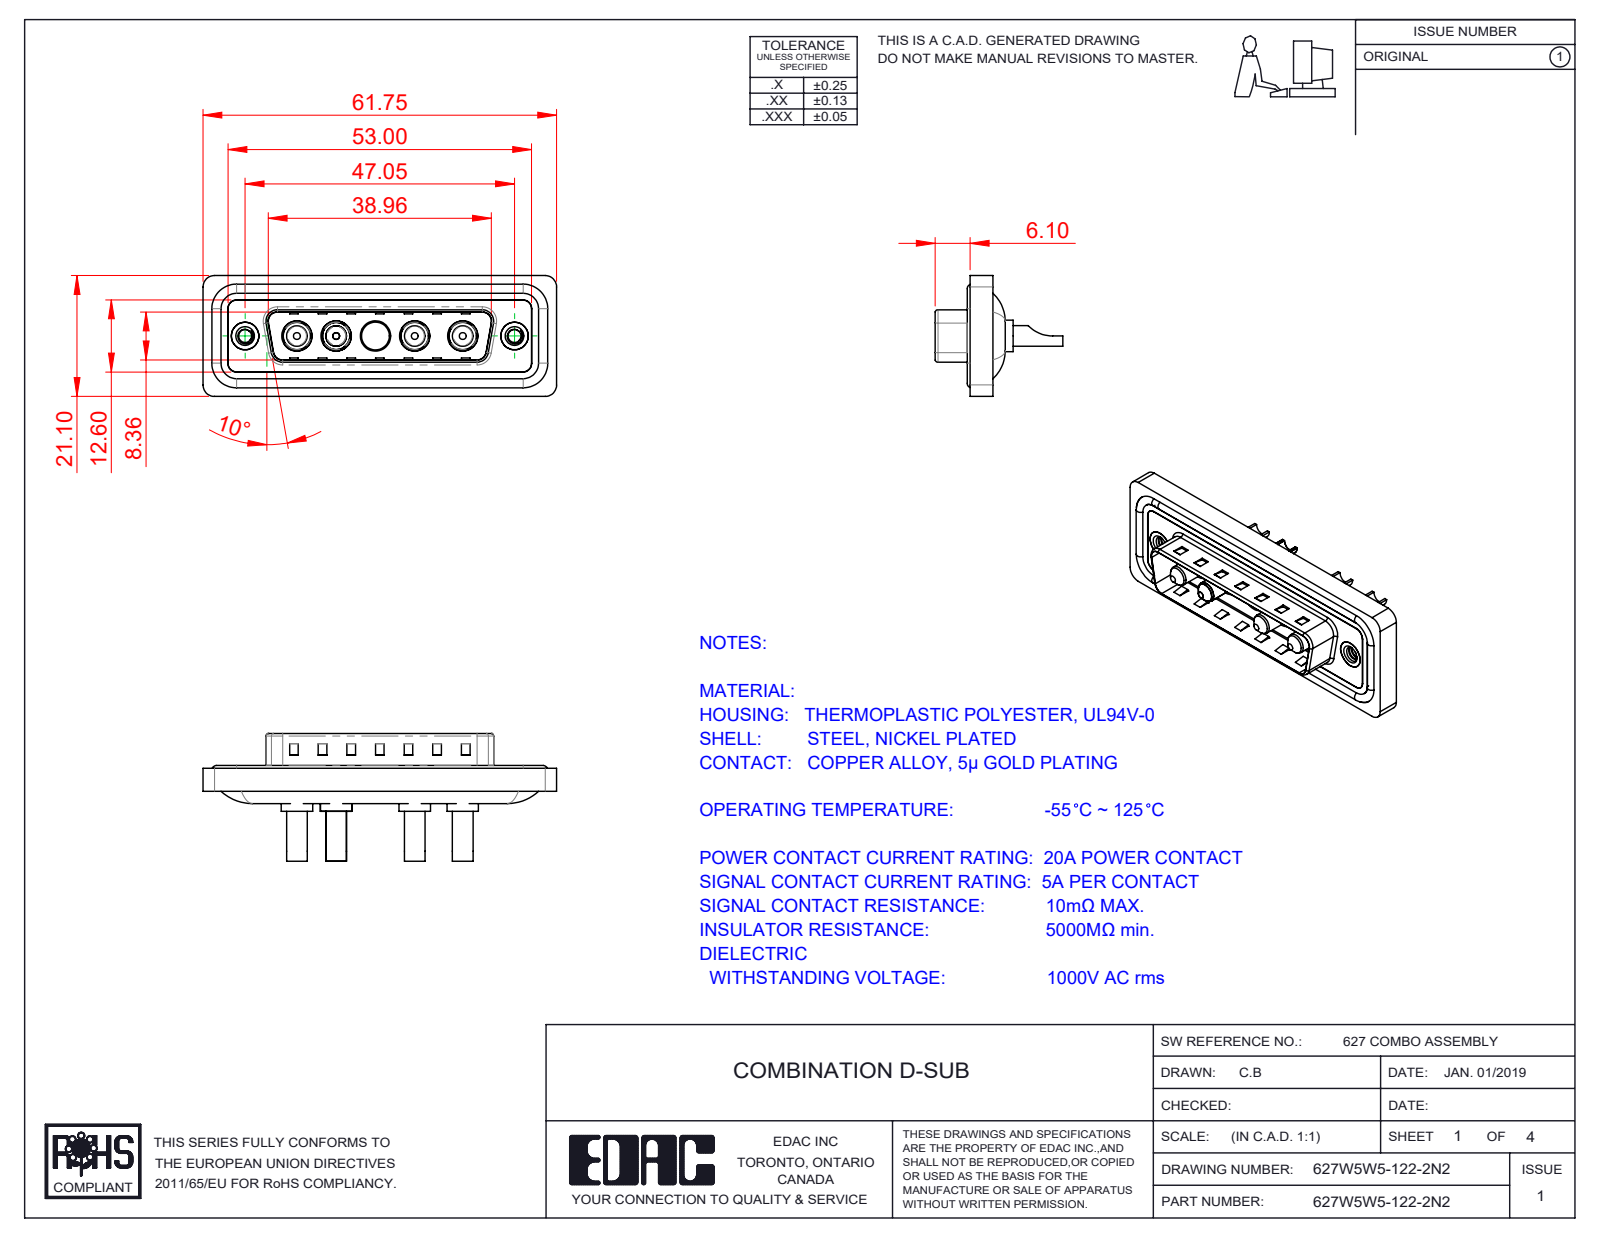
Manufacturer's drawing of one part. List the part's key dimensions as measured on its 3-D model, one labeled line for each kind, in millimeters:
Part name (STEP PRODUCT): 627W5W5-122-2N2; 627Combo Shell Front_25 Contacts; 627Combo Threaded Rivet_2; 627Combo Housing_5W5 (+3 more)
STEP written by: SolidWorks 2020 (CONFIG_CONTROL_DESIGN)
Units: millimetres
Bodies: 17 solids, 708 faces (274 planar, 298 cylindrical, 136 other)
Overall size (bounding box): 61.75 × 22.3 × 21.1
Volume: 7 537 mm³ · Surface area: 12 208 mm²
Round holes (diameter × count): ⌀4.85 ×5, ⌀5.3 ×5, ⌀2.7 ×4, ⌀2.26 ×2, ⌀4 ×2, ⌀4.8 ×2, ⌀5 ×2
Round bosses / shafts (diameter × count): ⌀5.5 ×4, ⌀5.2 ×4, ⌀4.75 ×4, ⌀3.75 ×4, ⌀3.6 ×4, ⌀1.6 ×4, ⌀4.9 ×2
Partial cylindrical surfaces — rounded edges, fillets, slot ends (radius × count): R1.5 ×22, R2 ×18, R0.5 ×8, R1.6 ×8, R0.25 ×4, R0.6 ×4, R0.65 ×4, R0.9 ×4
Main face-to-face distances: 0.4, 1.5, 0.5, 1.1, 3.1, 1.6, 2.9, 0.82, 9.58, 5.65
Hole centre spacings: 6.86, 9.04, 13.73, 38.01, 6.87, 8.37, 8.38, 9.05
